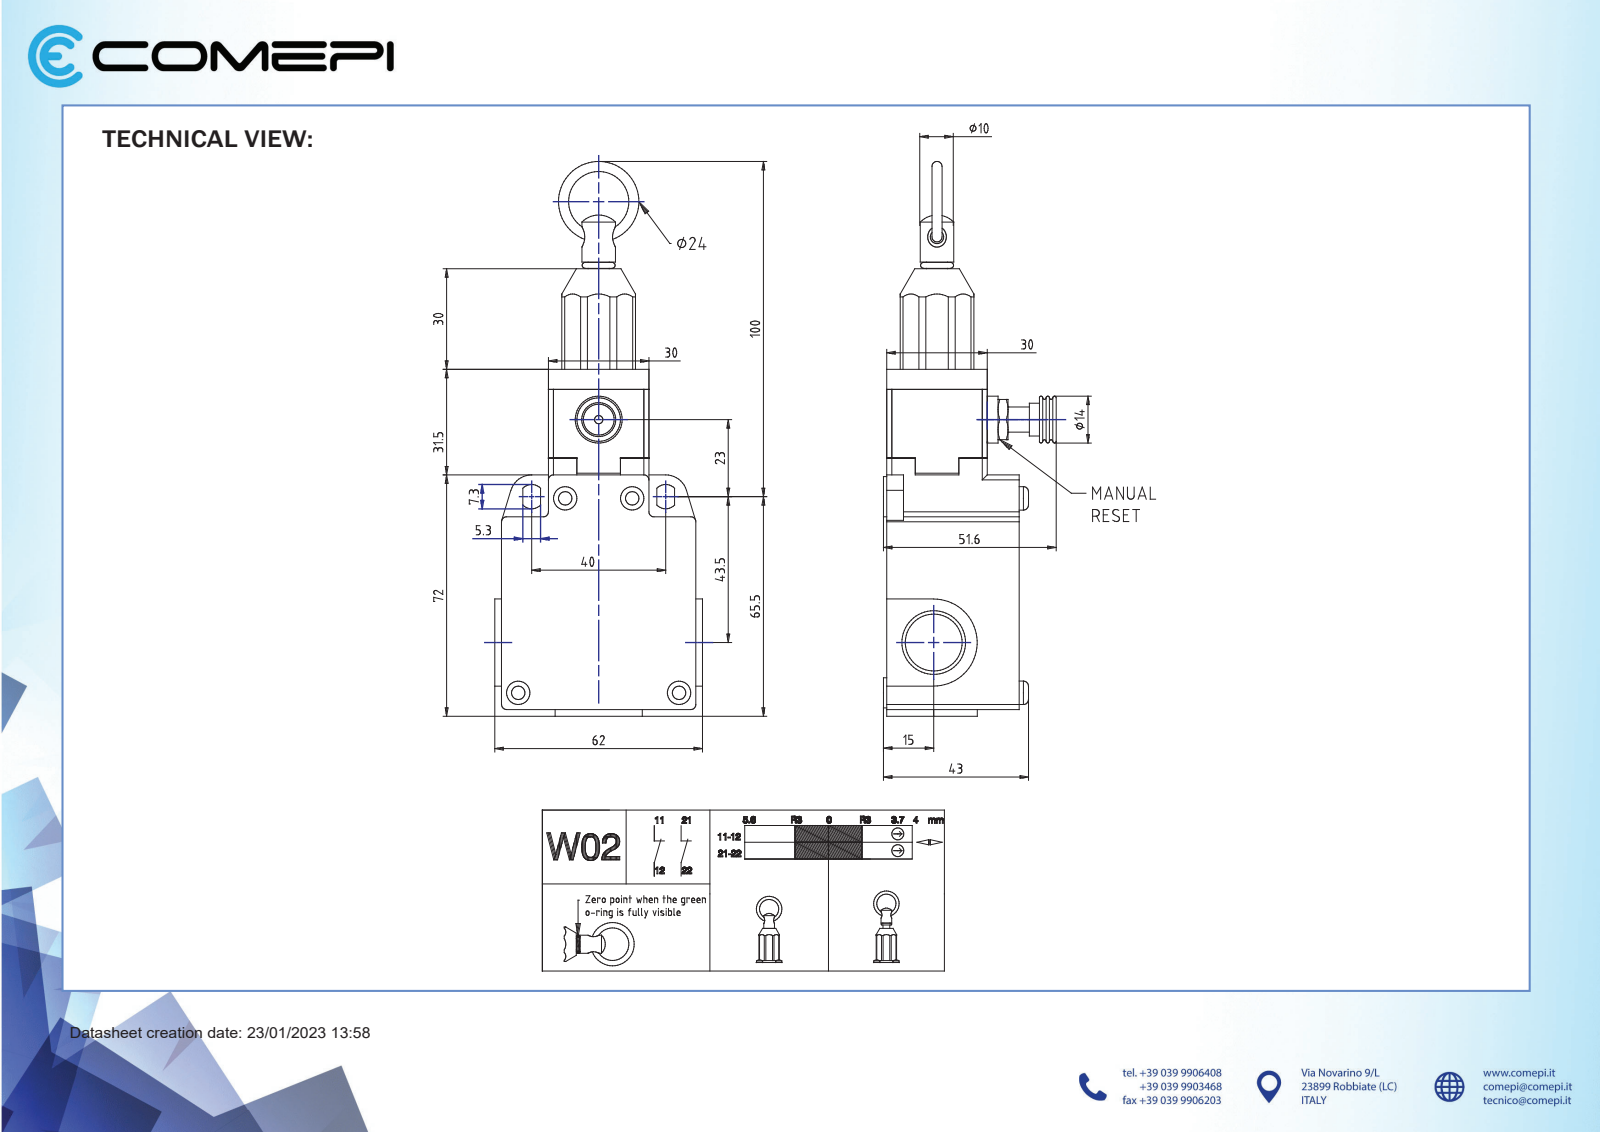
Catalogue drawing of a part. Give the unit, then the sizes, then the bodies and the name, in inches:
Units: inches
Overall size (bounding box): 6.619 × 2.598 × 1.673
Round holes (diameter × count): ⌀0.118 ×4, ⌀0.126 ×4, ⌀0.256 ×4, ⌀0.748 ×2, ⌀0.138 ×1, ⌀0.157 ×1, ⌀0.236 ×1, ⌀0.276 ×1, ⌀0.728 ×1
Round bosses / shafts (diameter × count): ⌀0.276 ×4, ⌀0.189 ×4, ⌀0.827 ×1, ⌀0.394 ×1, ⌀0.354 ×1, ⌀0.264 ×1, ⌀0.248 ×1, ⌀0.187 ×1
Partial cylindrical surfaces — rounded edges, fillets, slot ends (radius × count): R0.059 ×8, R0.039 ×5, R0.139 ×2, R0.256 ×2, R0.512 ×2
Main face-to-face distances: 1.583, 1.732, 0.551, 1.181, 2.283, 0.079, 0.039, 3.791, 0.197, 2.756
Hole centre spacings: 0.846, 0.575, 0.623, 1.022, 1.197, 2.272, 2.579, 3.286
Volume: 10.68 in³ · Surface area: 61.19 in²
Bodies: 3 solids, 445 faces (323 planar, 68 cylindrical, 54 other)
Part name (STEP PRODUCT): SCM2K9900W02
STEP written by: SolidWorks 2021 (AUTOMOTIVE_DESIGN)
